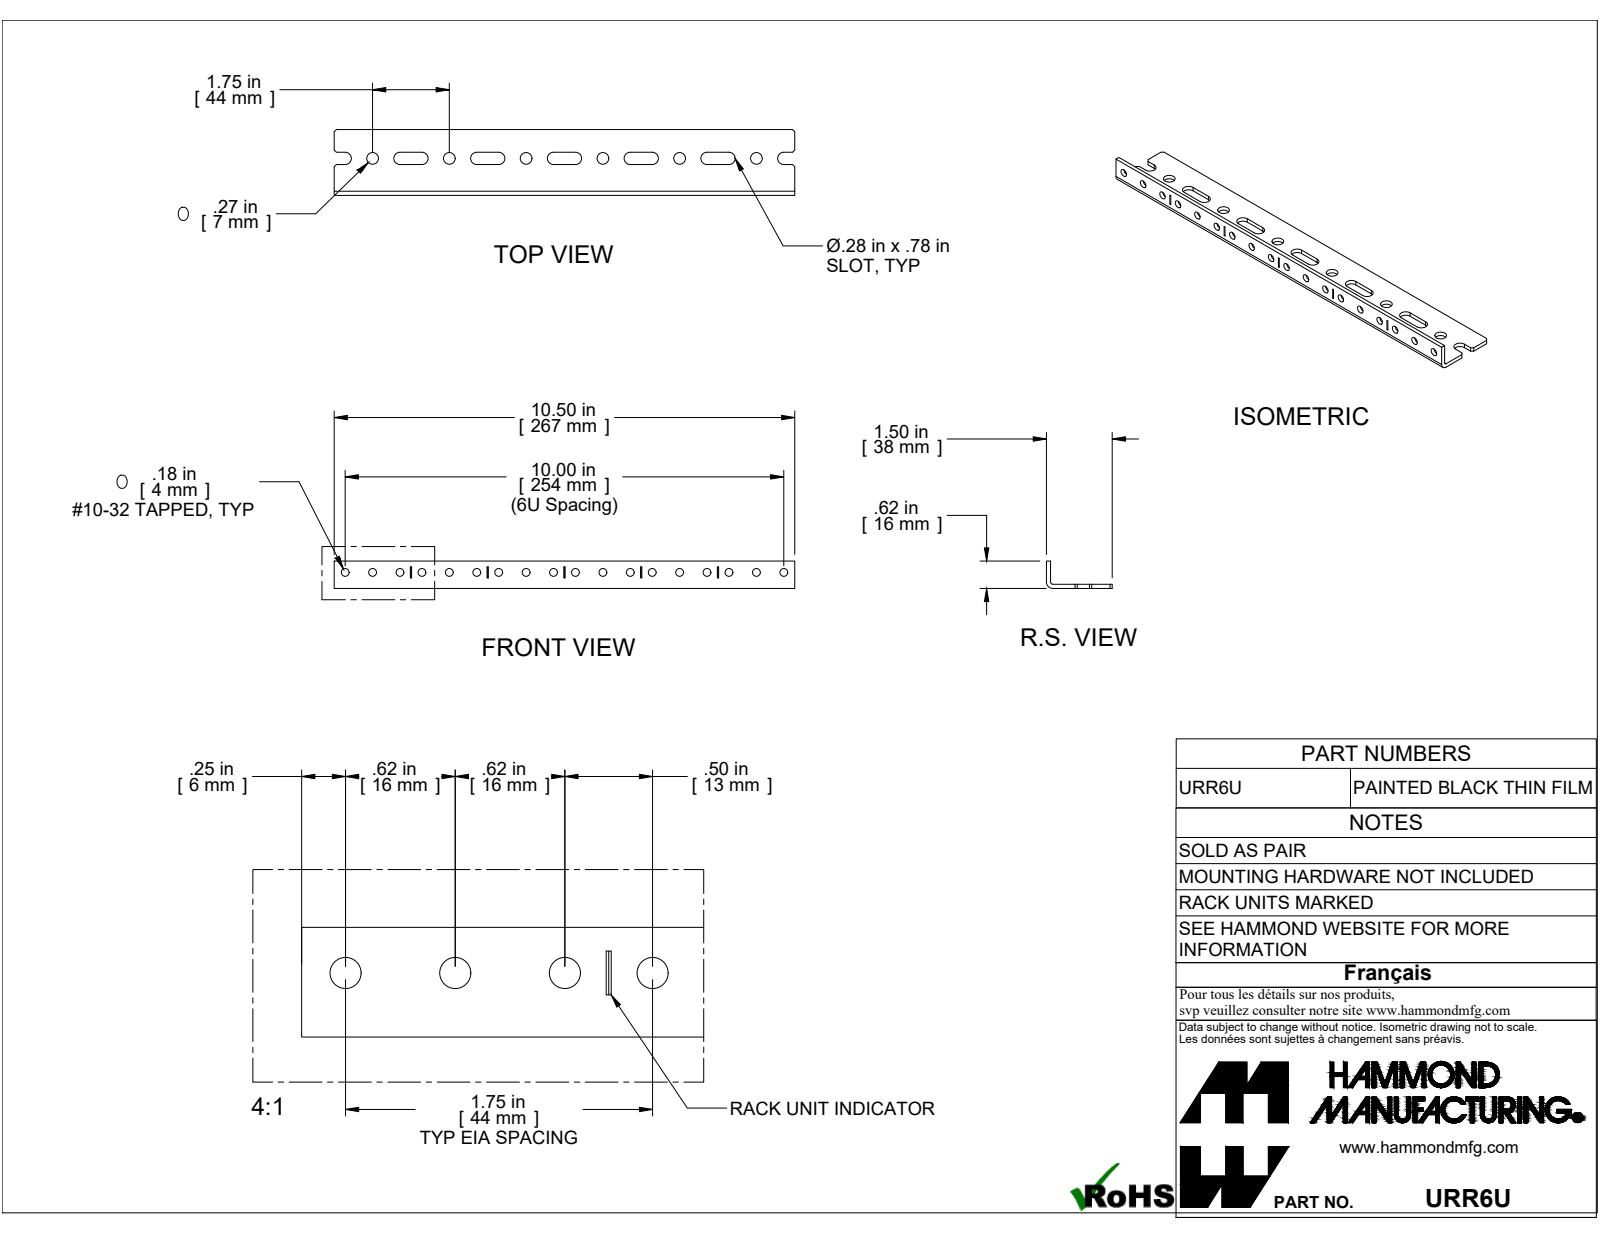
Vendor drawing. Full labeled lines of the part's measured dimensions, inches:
Part name (STEP PRODUCT): COM57213-6
STEP written by: ST-DEVELOPER v16.7 (AUTOMOTIVE_DESIGN)
Units: inches
Bodies: 1 solid, 88 faces (50 planar, 38 cylindrical, 0 other)
Overall size (bounding box): 10.5 × 1.5 × 0.625
Volume: 1.794 in³ · Surface area: 42.61 in²
Round holes (diameter × count): ⌀0.177 ×18, ⌀0.266 ×6
Partial cylindrical surfaces — rounded edges, fillets, slot ends (radius × count): R0.141 ×12, R0.048 ×1, R0.143 ×1
Main face-to-face distances: 0.095, 0.625, 0.53, 1.5, 1.405, 0.702, 0.607, 0.798, 0.983, 0.889
Hole centre spacings: 1.75, 3.5, 5.25, 0.625, 0.625, 1.125, 1.25, 2.375
